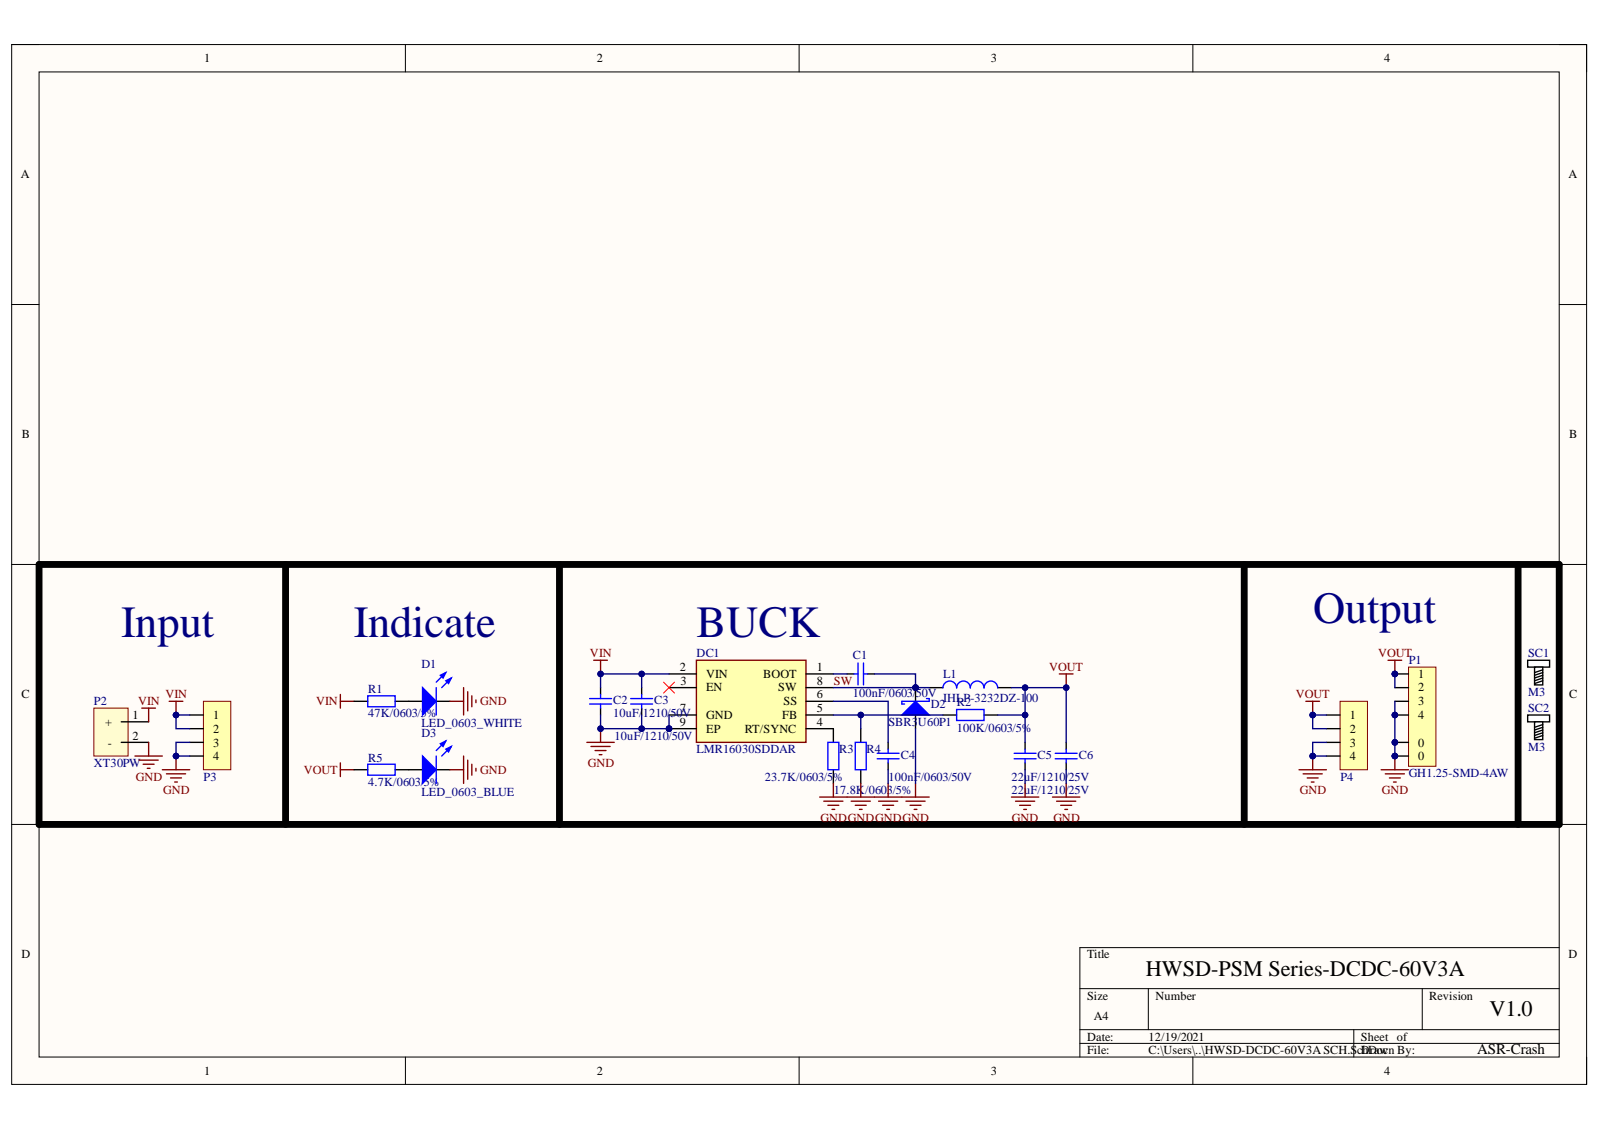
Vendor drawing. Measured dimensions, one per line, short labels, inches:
name: PCB; Board; L1; 5894088960 (+6 more)
written by: Open CASCADE 6.8 (AUTOMOTIVE_DESIGN)
unit: in
bodies: 54 solids, 1662 faces (1017 planar, 387 cylindrical, 258 other)
size: 1.575 × 0.787 × 0.414
volume: 0.139 in³; area: 6.372 in²
holes: 12× ⌀0.039, 2× ⌀0.036, 2× ⌀0.071, 2× ⌀0.118
bosses: 4× ⌀0.079, 2× ⌀0.098, 2× ⌀0.059, 2× ⌀0.039, 2× ⌀0.035
rounds: 63× R0.004, 52× R0.011, 8× R0.04, 6× R0.008, 4× R0.006, 4× R0.007, 4× R0.012, 4× R0.1
face distances: 0.067, 0.024, 0.098, 0.197, 0.075, 0.077, 0.173, 0.038, 0.062, 0.043
hole spacings: 0.1, 0.2, 0.657, 0.504, 0.665, 0.665, 0.261, 0.3
